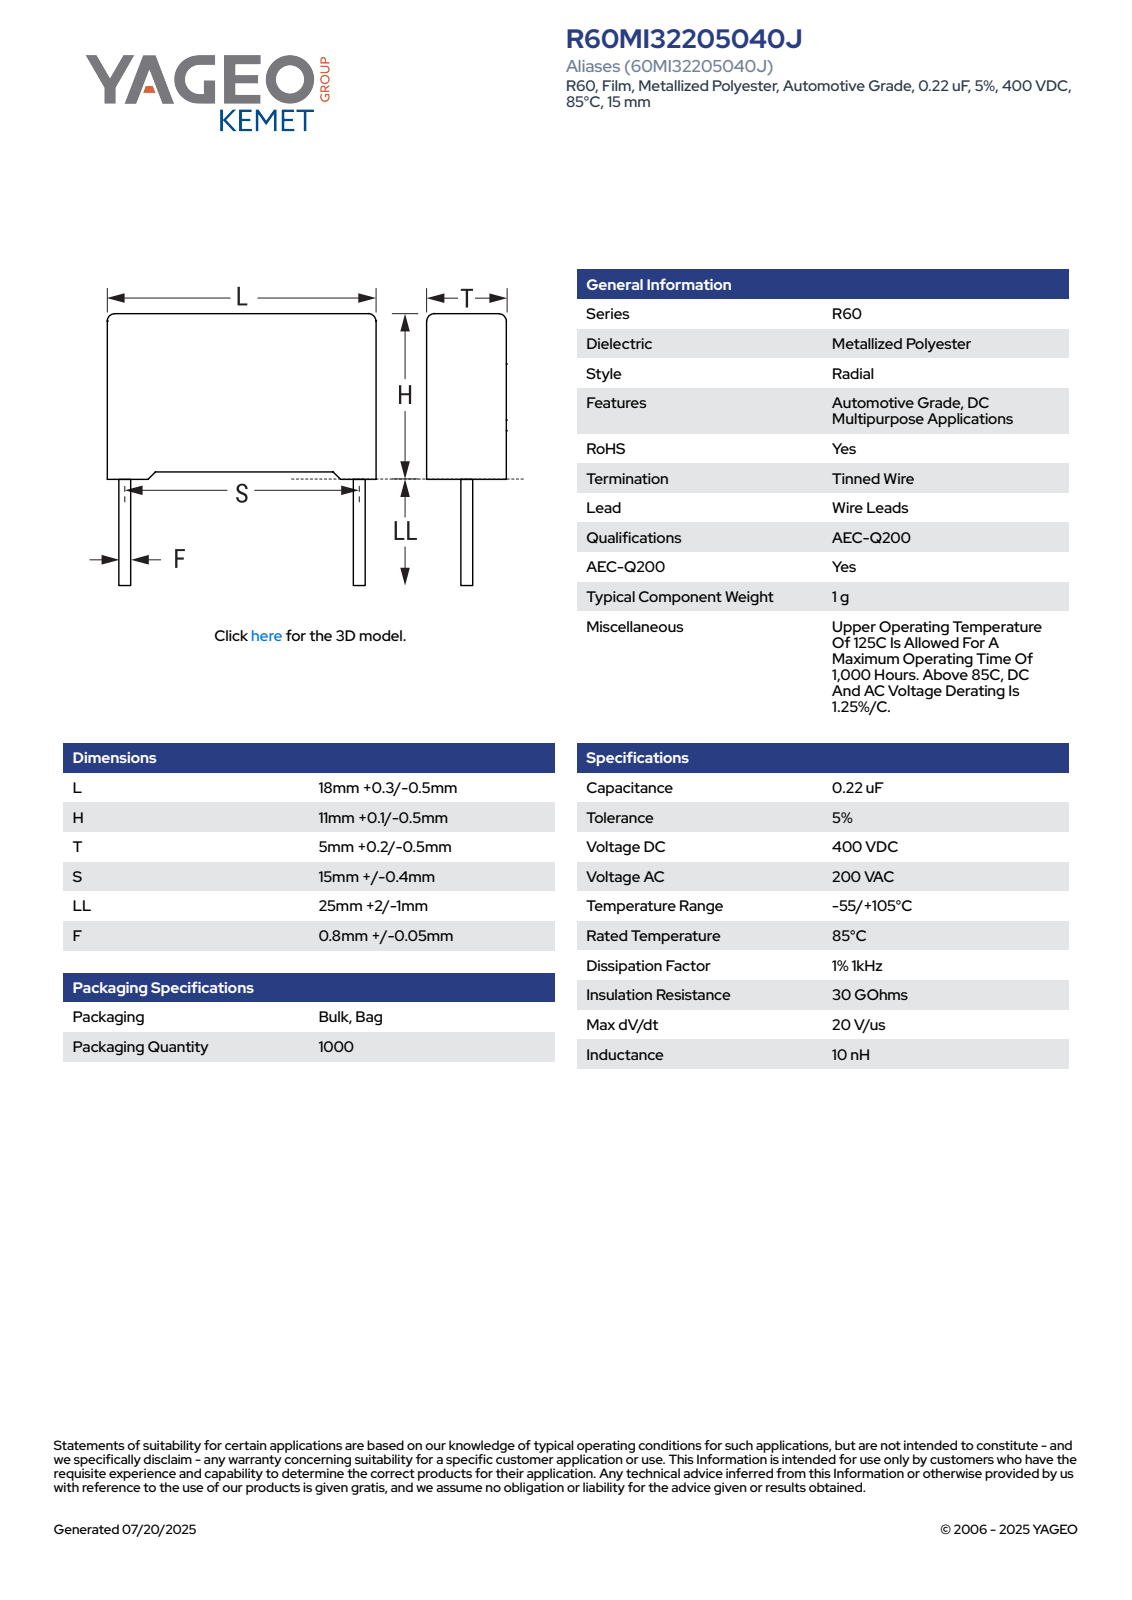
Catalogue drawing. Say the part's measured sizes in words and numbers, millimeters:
The part is named "CFR_RB2_18X11X5_L18.3H11.1T5.2S15LL27F0.85". Its 3-D file was written by "SolidWorks 2021 (AUTOMOTIVE_DESIGN)". It is 4 solids with 85 faces: 77 planar, 8 cylindrical and 0 other. Overall it measures 38.1 by 18.3 by 5.21 millimeters. Its volume is 1 029 cubic millimeters and its surface area 890 square millimeters. Round bosses or shafts: 2 of diameter 0.85. Partial cylindrical surfaces (rounded edges, fillets, slot ends): 4 of radius 0.5. The main face-to-face distances are 5.2, 10.35, 18.3, 0.61, 4.59, 0.37, 10.72, 0.38, 0.75, 11.1.
